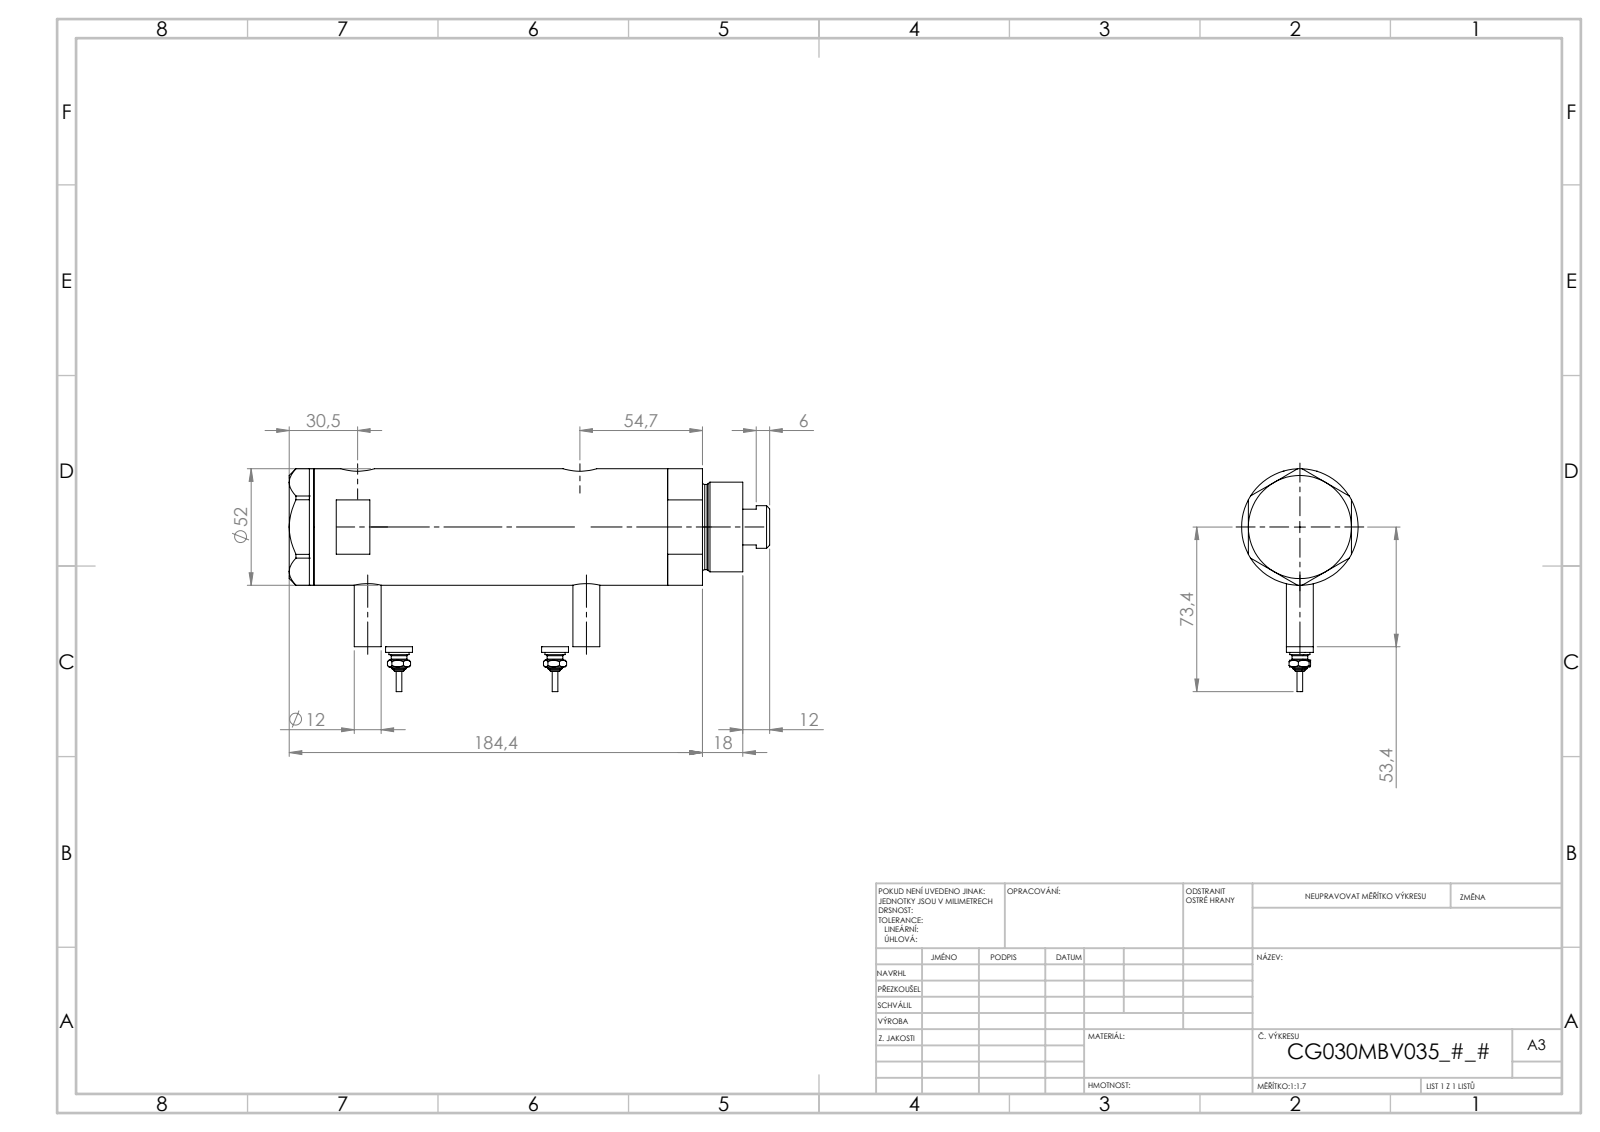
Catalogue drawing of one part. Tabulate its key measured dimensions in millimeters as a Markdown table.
| quantity | value |
| --- | --- |
| part name | V270CG_MIDDLE; V270CG_BACK; V270CG_FRONT; V270CG_VC (+1 more) |
| STEP written by | SolidWorks 2019 (CONFIG_CONTROL_DESIGN) |
| units | millimeters |
| bodies | 6 solids, 246 faces (95 planar, 77 cylindrical, 74 other) |
| overall size | 184.02 × 84.3 × 52 |
| volume | 330 961 mm³ |
| surface area | 78 252 mm² |
| round holes (diameter × count) | 5 × 2, 9.73 × 2, 12.5 × 2, 15 × 2, 6.5 × 1, 20 × 1, 21.5 × 1, 30 × 1, 33 × 1, 44 × 1 |
| round bosses / shafts (diameter × count) | 12 × 3, 9 × 2, 7 × 2, 4.34 × 2, 2.4 × 2, 52 × 1, 40 × 1, 38 × 1 |
| main face-to-face distances | 23.8, 11, 34.8, 46, 99.56, 88.56, 64.76, 135.96, 124.96, 101.16 |
| hole center spacings | 2.9, 4.5, 61.75, 64.65, 66.25, 69.15, 2.89, 2.91 |
